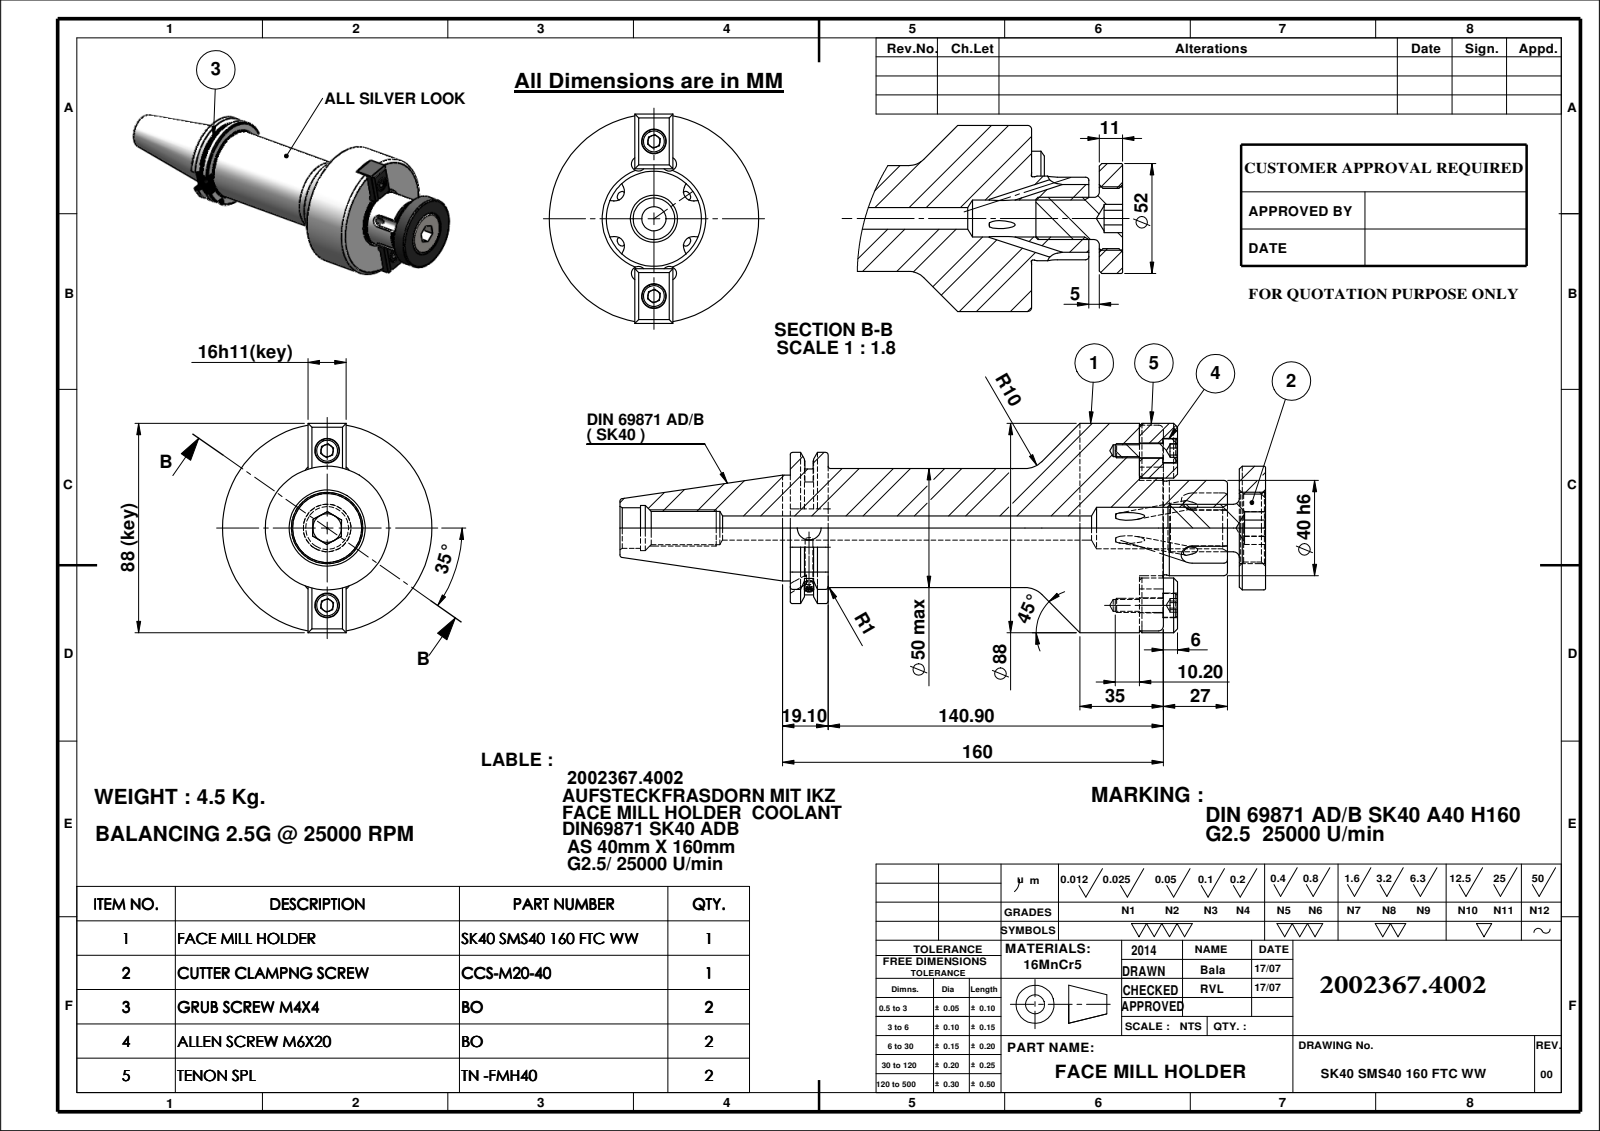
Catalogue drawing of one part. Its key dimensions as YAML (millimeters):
part_name: "TN -FMH40; AS-M6X20._PreviewCfg; SK40 SMS40 160 FTC WW; M4X4_DIN 913 - M4 x 4-N"
step_written_by: "SolidWorks 2009 (CONFIG_CONTROL_DESIGN)"
units: millimeters
bodies: {solids: 7, faces: 313, planar: 124, cylindrical: 84, other: 105}
overall_size: [255.4, 88, 88]
volume: 569646
surface_area: 72392
round_holes:
  - {diameter: 4, count: 4}
  - {diameter: 5, count: 2}
  - {diameter: 6.4, count: 2}
  - {diameter: 10.4, count: 2}
  - {diameter: 3.3, count: 1}
  - {diameter: 10, count: 1}
  - {diameter: 10.2, count: 1}
  - {diameter: 14, count: 1}
  - {diameter: 17, count: 1}
  - {diameter: 17.5, count: 1}
  - {diameter: 19, count: 1}
round_bosses_or_shafts:
  - {diameter: 10, count: 2}
  - {diameter: 6, count: 2}
  - {diameter: 4, count: 2}
  - {diameter: 88, count: 1}
  - {diameter: 50, count: 1}
  - {diameter: 44.45, count: 1}
  - {diameter: 40, count: 1}
  - {diameter: 39.4, count: 1}
partial_cylinders:
  - {radius: 3, count: 4}
  - {radius: 4, count: 4}
  - {radius: 28.12, count: 1}
  - {radius: 31.77, count: 1}
face_to_face_distances: [16, 10, 146.8, 156.8, 183.8, 37, 27, 15.9, 130.9, 140.9]
hole_center_spacings: [32.5, 65]
